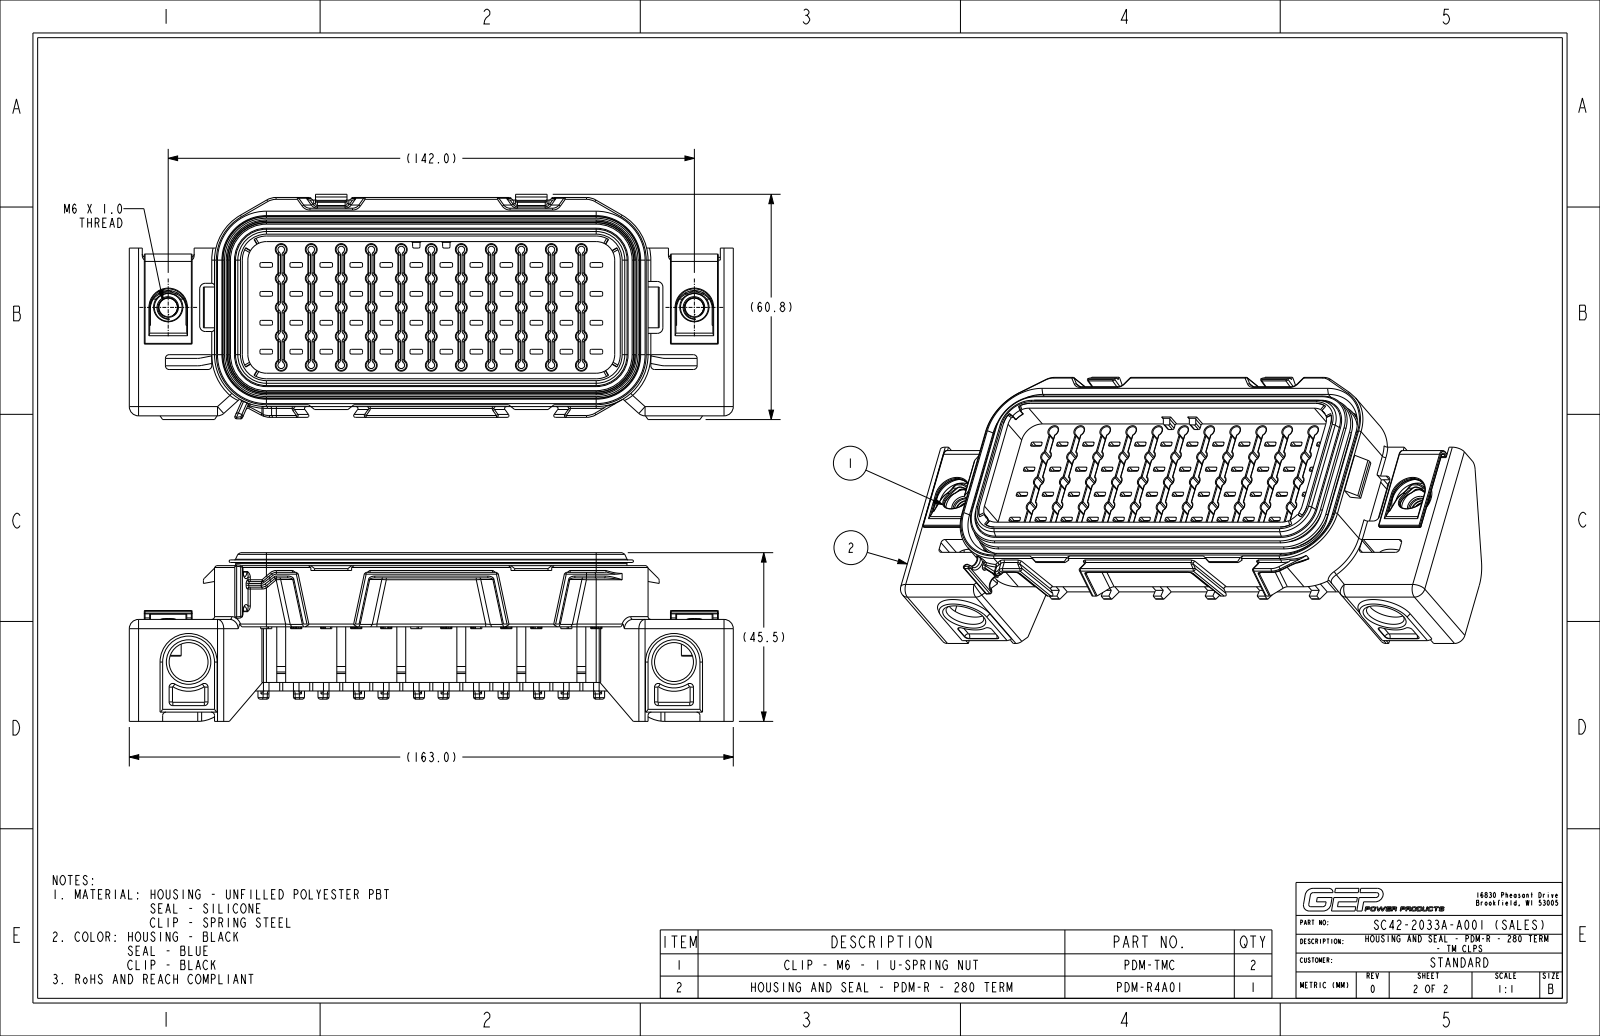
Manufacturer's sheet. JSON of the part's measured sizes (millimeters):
{"part_name": "C26-1012-2A_NCF_FOR_SALES_STP; C14-1013_INSTALLED_NCF; PDM-RS_INSTALLED_NCF_ASM; PDM-R4A01_NCF_ASM (+3 more)", "step_written_by": "CREO PARAMETRIC BY PTC INC, 2024014 (CONFIG_CONTROL_DESIGN)", "units": "millimeters", "bodies": {"solids": 4, "faces": 6945, "planar": 2965, "cylindrical": 1932, "other": 2048}, "overall_size": [163, 60.76, 45.5], "volume_mm3": 123736, "surface_area_mm2": 107538, "round_holes": [[6.7, 48], [10.5, 4], [5, 2], [7.5, 2], [12.5, 2]], "round_bosses_or_shafts": [[7, 2], [5, 1], [2.5, 1]], "partial_cylinders_radius": [[0.5, 549], [0.4, 205], [0.8, 158], [0.2, 68], [1.4, 55], [4.45, 48], [0.3, 46], [0.9, 39]], "face_to_face_distances": [2, 1.5, 38.5, 37, 1.8, 7, 5.5, 9.5, 11.5, 9], "hole_center_spacings": [11.24, 17.98, 7.8, 8.1, 17.58, 25.52, 33.33, 16.2]}
